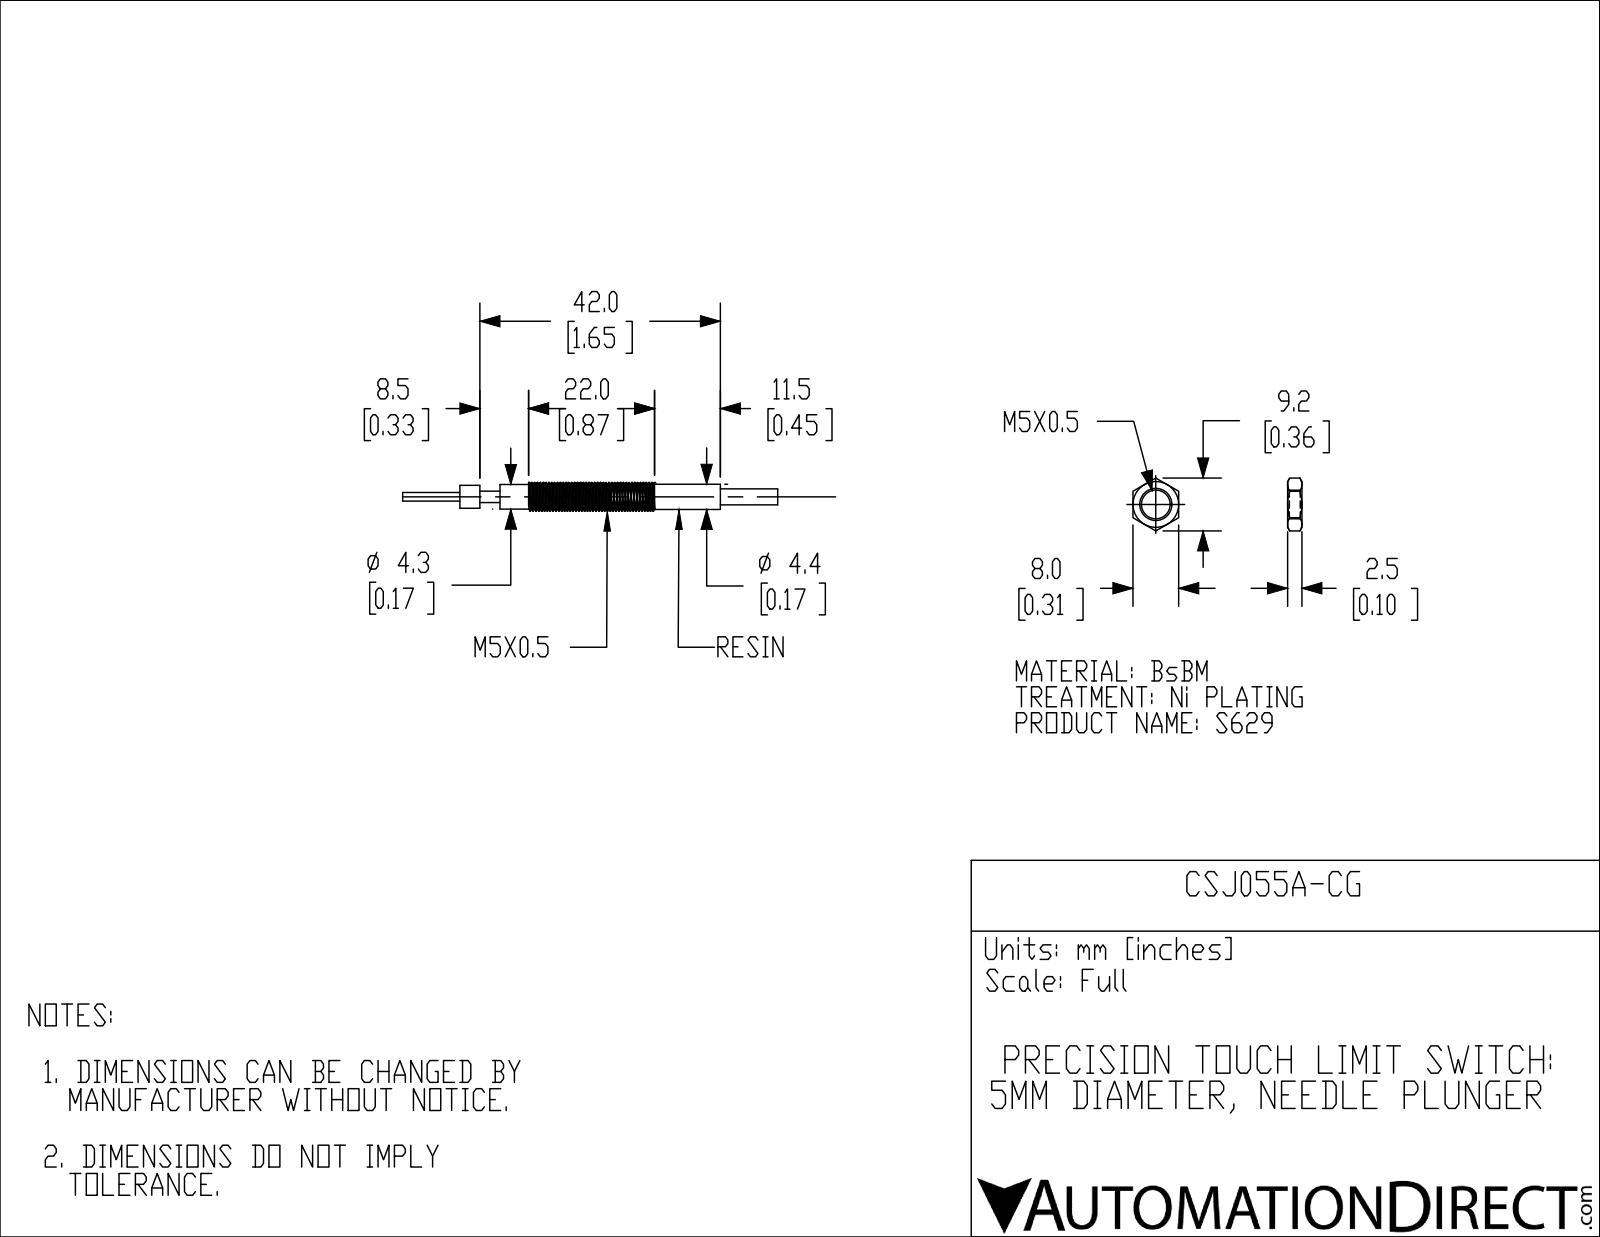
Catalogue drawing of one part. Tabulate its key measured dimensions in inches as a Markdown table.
| quantity | value |
| --- | --- |
| part name | CSJ055A-CG |
| STEP written by | SolidWorks 2018 (AUTOMOTIVE_DESIGN) |
| units | inches |
| bodies | 1 solid, 23 faces (14 planar, 7 cylindrical, 2 other) |
| overall size | 2.579 × 0.197 × 0.197 |
| volume | 0.049 in³ |
| surface area | 1.286 in² |
| round bosses / shafts (diameter × count) | 0.197 × 1, 0.173 × 1, 0.169 × 1, 0.157 × 1, 0.11 × 1, 0.079 × 1, 0.059 × 1 |
| main face-to-face distances | 0.138, 0.173, 0.276, 1.791, 1.654, 1.516, 0.394, 2.185, 2.047, 1.909 |
